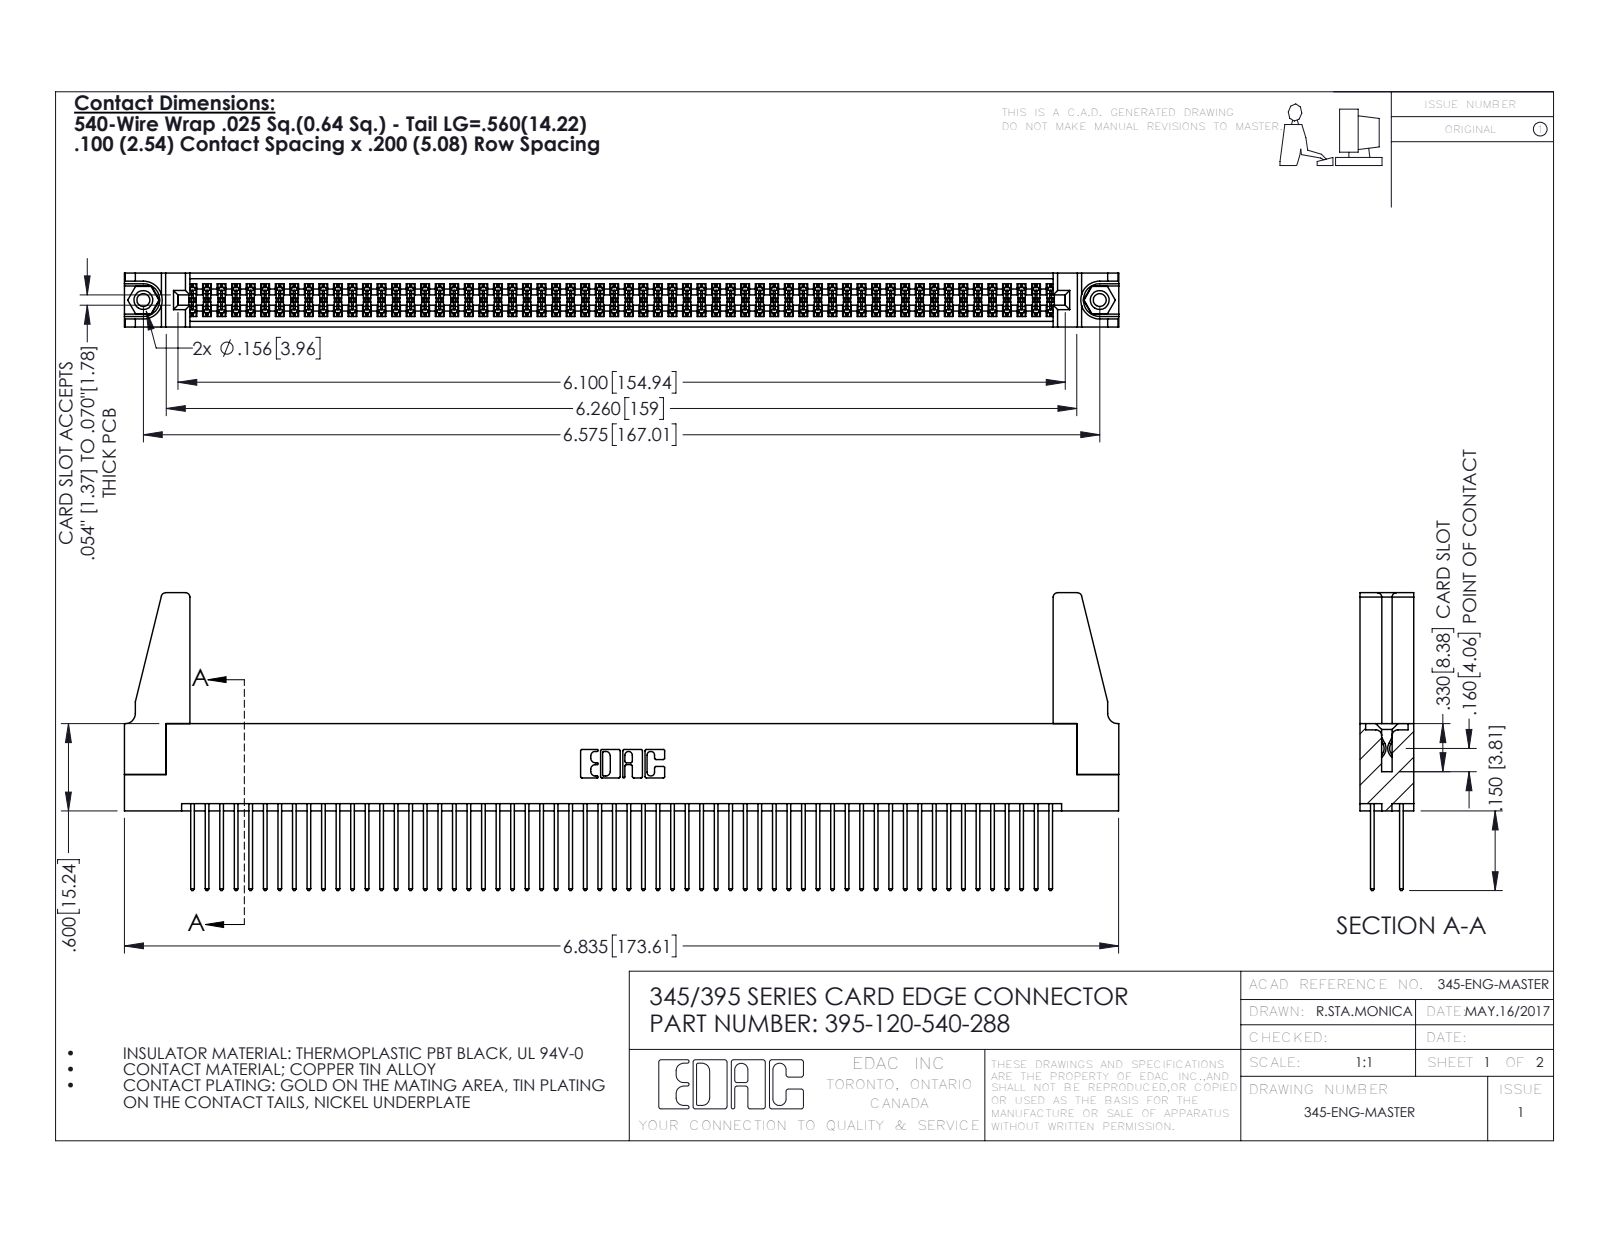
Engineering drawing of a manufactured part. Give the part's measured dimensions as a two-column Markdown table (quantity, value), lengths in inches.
| quantity | value |
| --- | --- |
| part name | 345 Part_Flush Mounting Lugs - 0.156 Dia-TH; 345-250-001_345-250-001-102; 395-120-540-288; 345-220-078_345-220-088 (+1 more) |
| STEP written by | SolidWorks 2016 (CONFIG_CONTROL_DESIGN) |
| units | inches |
| bodies | 125 solids, 6250 faces (4112 planar, 2122 cylindrical, 16 other) |
| overall size | 6.836 × 2.047 × 0.37 |
| volume | 1.266 in³ |
| surface area | 48.72 in² |
| round holes (diameter × count) | 0.089 × 2, 0.125 × 2, 0.156 × 2, 0.064 × 1 |
| round bosses / shafts (diameter × count) | 0.155 × 2 |
| partial cylindrical surfaces (radius × count) | 0.006 × 180, 0.01 × 120, 0.01 × 22, 0.03 × 8, 0.007 × 6, 0.031 × 6, 0.026 × 3, 0.014 × 2 |
| main face-to-face distances | 0.072, 0.298, 0.2, 0.098, 0.272, 0.025, 0.37, 0.225, 0.175, 0.149 |
| hole center spacings | 0.27, 6.339, 6.575 |
